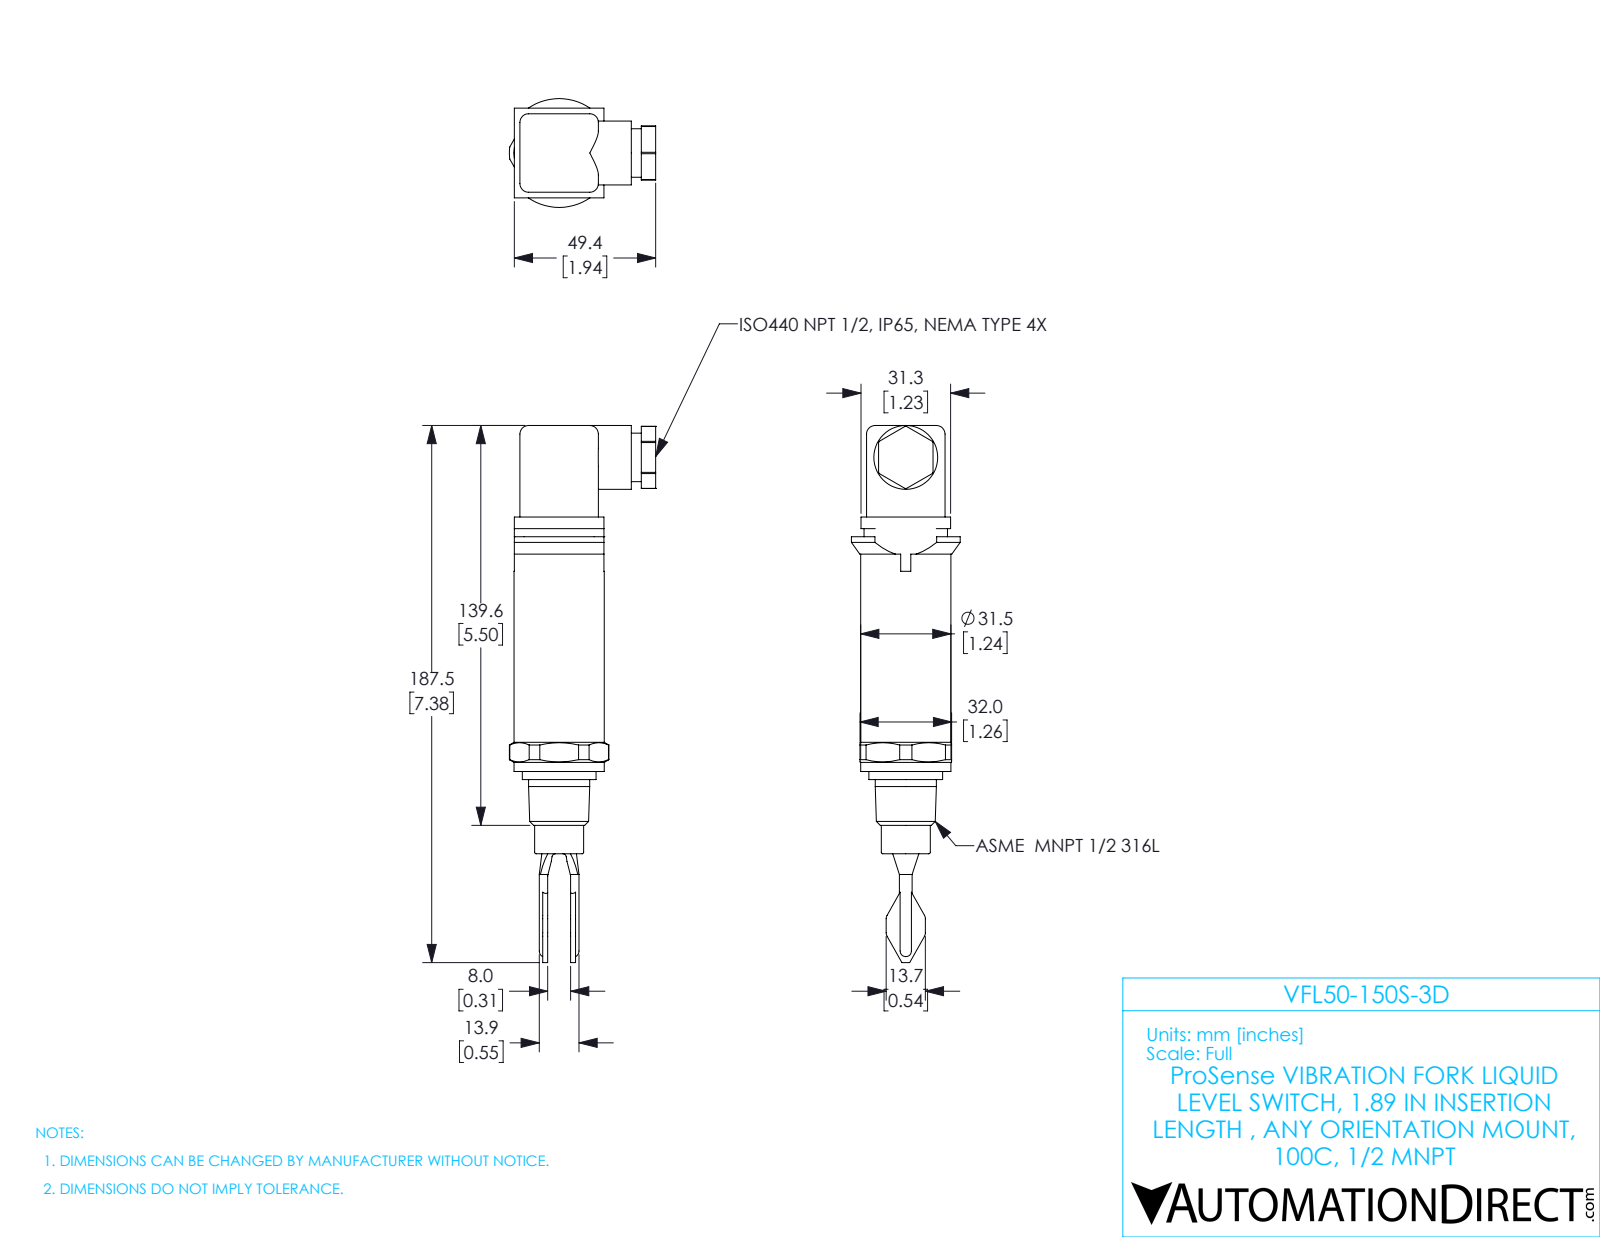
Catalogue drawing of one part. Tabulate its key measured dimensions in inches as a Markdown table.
| quantity | value |
| --- | --- |
| part name | VFL50-150S-3D |
| STEP written by | SolidWorks 2017 (AUTOMOTIVE_DESIGN) |
| units | inches |
| bodies | 1 solid, 158 faces (79 planar, 58 cylindrical, 21 other) |
| overall size | 7.382 × 2.011 × 1.496 |
| volume | 6.903 in³ |
| surface area | 29.88 in² |
| round bosses / shafts (diameter × count) | 1.24 × 1, 1.014 × 1, 0.878 × 1, 0.84 × 1, 0.673 × 1, 0.667 × 1 |
| partial cylindrical surfaces (radius × count) | 0.119 × 8, 0.047 × 4, 0.094 × 4, 0.154 × 4, 0.088 × 2, 0.426 × 1, 0.684 × 1, 0.748 × 1 |
| main face-to-face distances | 1.079, 0.077, 1.156, 0.459, 0.774, 0.382, 0.697, 1.232, 1.169, 1.943 |
